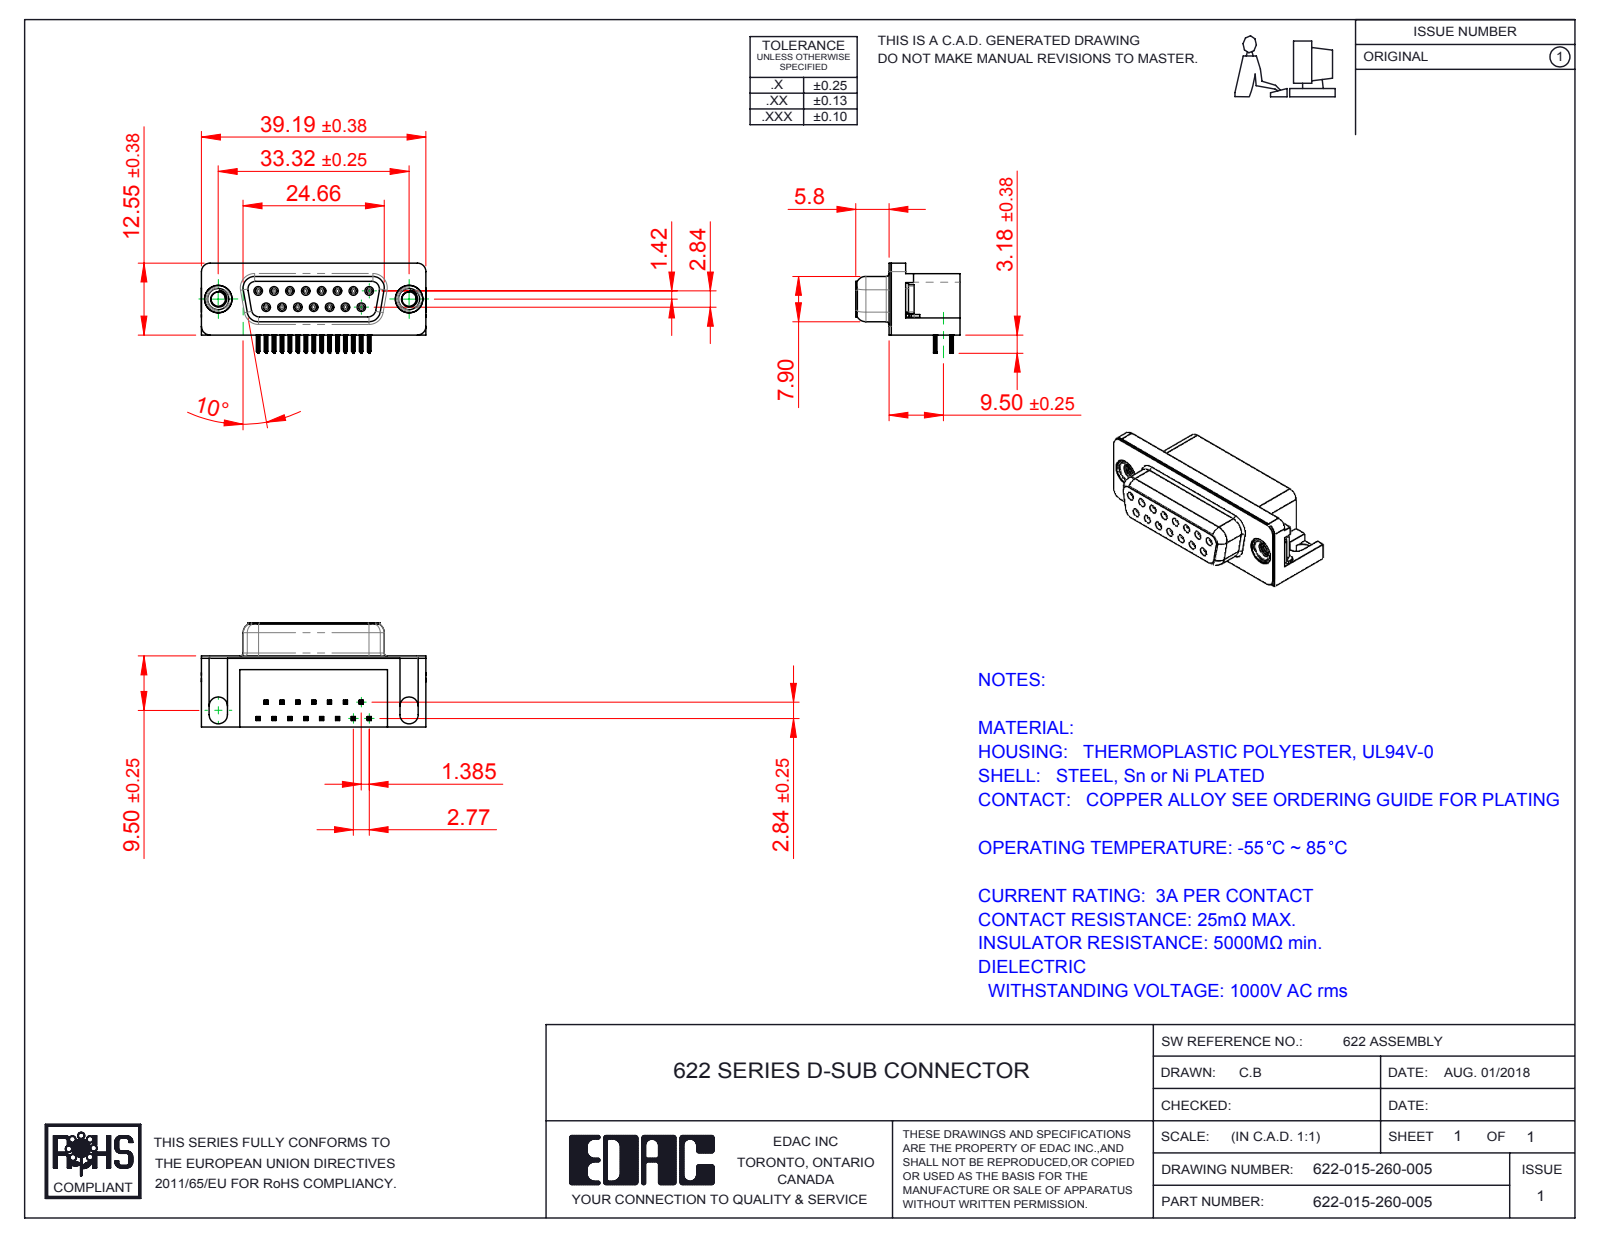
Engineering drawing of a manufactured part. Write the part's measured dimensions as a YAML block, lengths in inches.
part_name: "622 Contact Top; 622 Non Board Mount; 622 Socket Bottom; 622 Housing_15 Socket (+3 more)"
step_written_by: "SolidWorks 2016 (CONFIG_CONTROL_DESIGN)"
units: inches
bodies: {solids: 21, faces: 2423, planar: 1074, cylindrical: 605, other: 744}
overall_size: [1.544, 0.717, 0.619]
volume: 0.314
surface_area: 10.15
round_holes:
  - {diameter: 0.031, count: 15}
  - {diameter: 0.035, count: 15}
  - {diameter: 0.098, count: 2}
  - {diameter: 0.157, count: 2}
  - {diameter: 0.189, count: 2}
  - {diameter: 0.197, count: 2}
round_bosses_or_shafts:
  - {diameter: 0.047, count: 15}
  - {diameter: 0.193, count: 2}
  - {diameter: 0.187, count: 2}
  - {diameter: 0.154, count: 2}
partial_cylinders:
  - {radius: 0.004, count: 120}
  - {radius: 0.006, count: 60}
  - {radius: 0.014, count: 30}
  - {radius: 0.039, count: 18}
  - {radius: 0.013, count: 15}
  - {radius: 0.01, count: 8}
  - {radius: 0.053, count: 8}
  - {radius: 0.059, count: 8}
face_to_face_distances: [0.016, 0.472, 0.244, 0.488, 0.407, 0.114, 0.374, 0.098, 0.014, 0.018]
hole_center_spacings: [0.124, 0.109, 0.218, 0.327, 0.436, 0.198, 0.198, 0.294]
